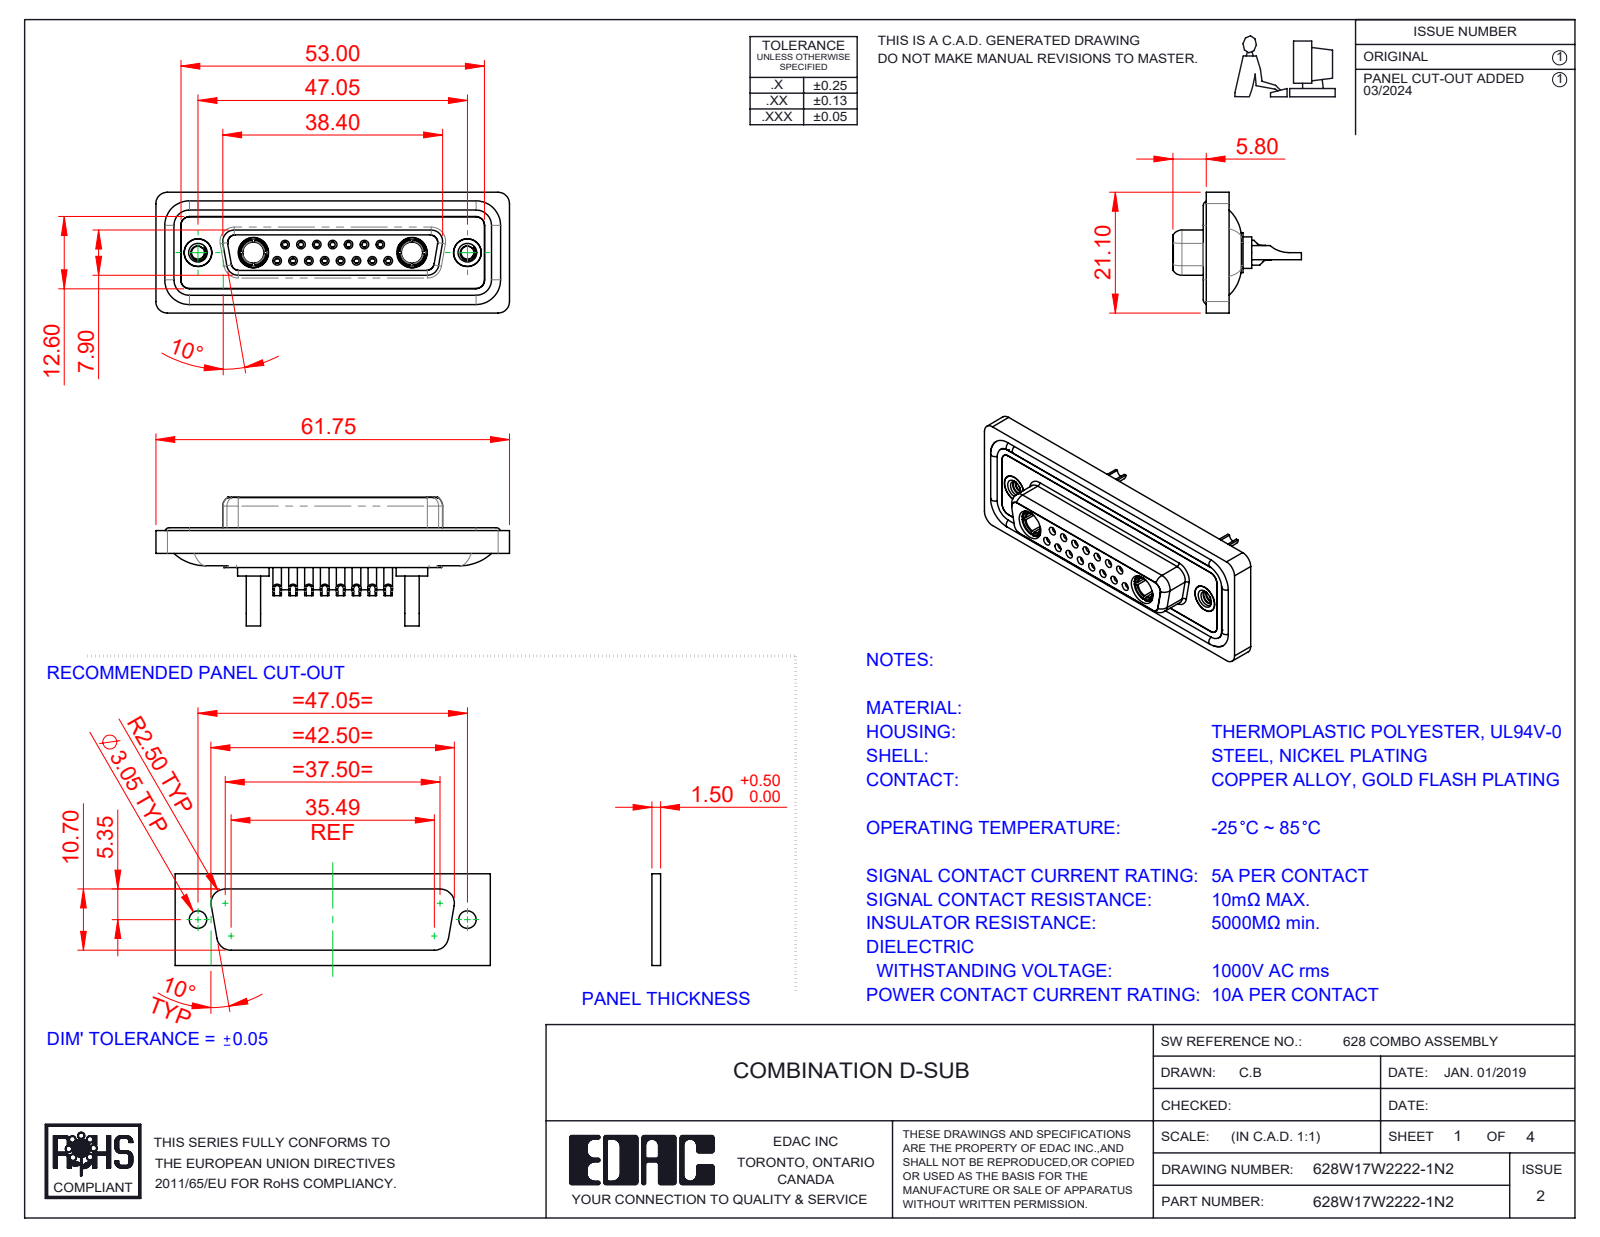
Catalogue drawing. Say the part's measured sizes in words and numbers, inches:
The part is named "628W17W2222-1N2; Power Socket_10A SC; 628Combo Contact Row 1_22; 628Combo Shell Front_25 Contacts (+5 more)". Its 3-D file was written by "SolidWorks 2023 (CONFIG_CONTROL_DESIGN)". It is 26 solids with 1369 faces: 422 planar, 555 cylindrical and 392 other. Overall it measures 2.431 by 0.884 by 0.831 inches. Its volume is 0.51 cubic inches and its surface area 21.87 square inches. Round holes: 15 of diameter 0.035, 15 of diameter 0.039, 15 of diameter 0.043, 15 of diameter 0.059, 15 of diameter 0.079, 8 of diameter 0.063, 7 of diameter 0.067, 4 of diameter 0.191, 2 of diameter 0.067, 2 of diameter 0.089, 2 of diameter 0.146, 2 of diameter 0.157. Round bosses or shafts: 15 of diameter 0.087, 11 of diameter 0.063, 2 of diameter 0.217, 2 of diameter 0.205, 2 of diameter 0.195, 2 of diameter 0.195, 2 of diameter 0.189, 2 of diameter 0.187. Partial cylindrical surfaces (rounded edges, fillets, slot ends): 22 of radius 0.059, 18 of radius 0.079, 8 of radius 0.053, 8 of radius 0.063, 6 of radius 0.039, 4 of radius 0.01, 4 of radius 0.02, 4 of radius 0.024. The main face-to-face distances are 0.016, 0.071, 0.293, 0.222, 0.26, 0.02, 0.278, 0.063, 0.114, 0.043. The hole center spacings are 0.124, 0.109, 0.327, 0.218, 0.198, 0.198, 0.295, 0.436.
